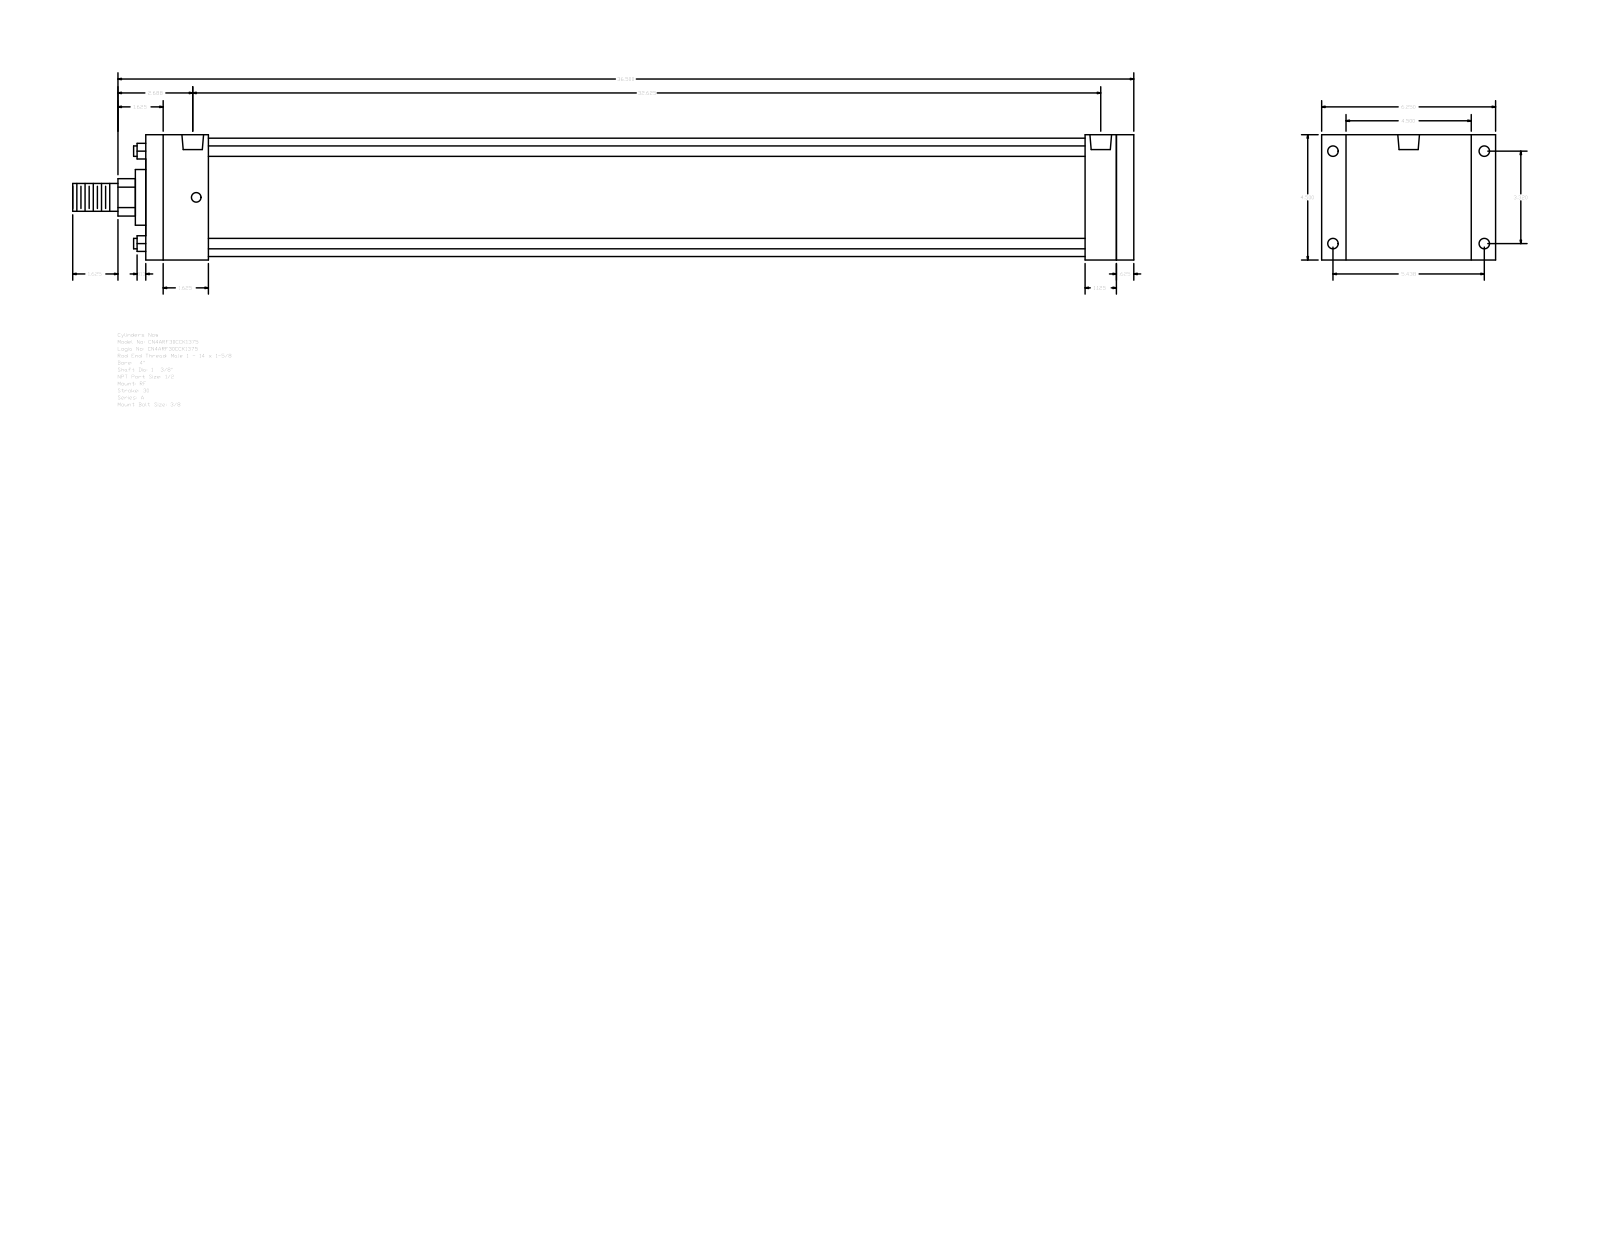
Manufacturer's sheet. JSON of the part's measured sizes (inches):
{"part_name": "A_RF__0400_1.375", "step_written_by": "GSSL Pune (CONFIG_CONTROL_DESIGN)", "units": "inches", "bodies": {"solids": 0, "faces": 92, "planar": 64, "cylindrical": 28, "other": 0}, "overall_size": [38.125, 6.25, 4.5], "round_holes": [[0.344, 4], [0.375, 4], [0.778, 2]], "round_bosses_or_shafts": [[0.375, 4], [4.25, 1], [2, 1], [1.375, 1], [1, 1]], "partial_cylinders_radius": [[0.672, 1]], "face_to_face_distances": [4.5, 35.5, 34.875, 0.625, 2.25, 1.125, 0.875, 5.375, 33.75, 1.75], "hole_center_spacings": [0.125, 3.32, 5.438, 6.371, 32.375, 32.5, 32.625]}
